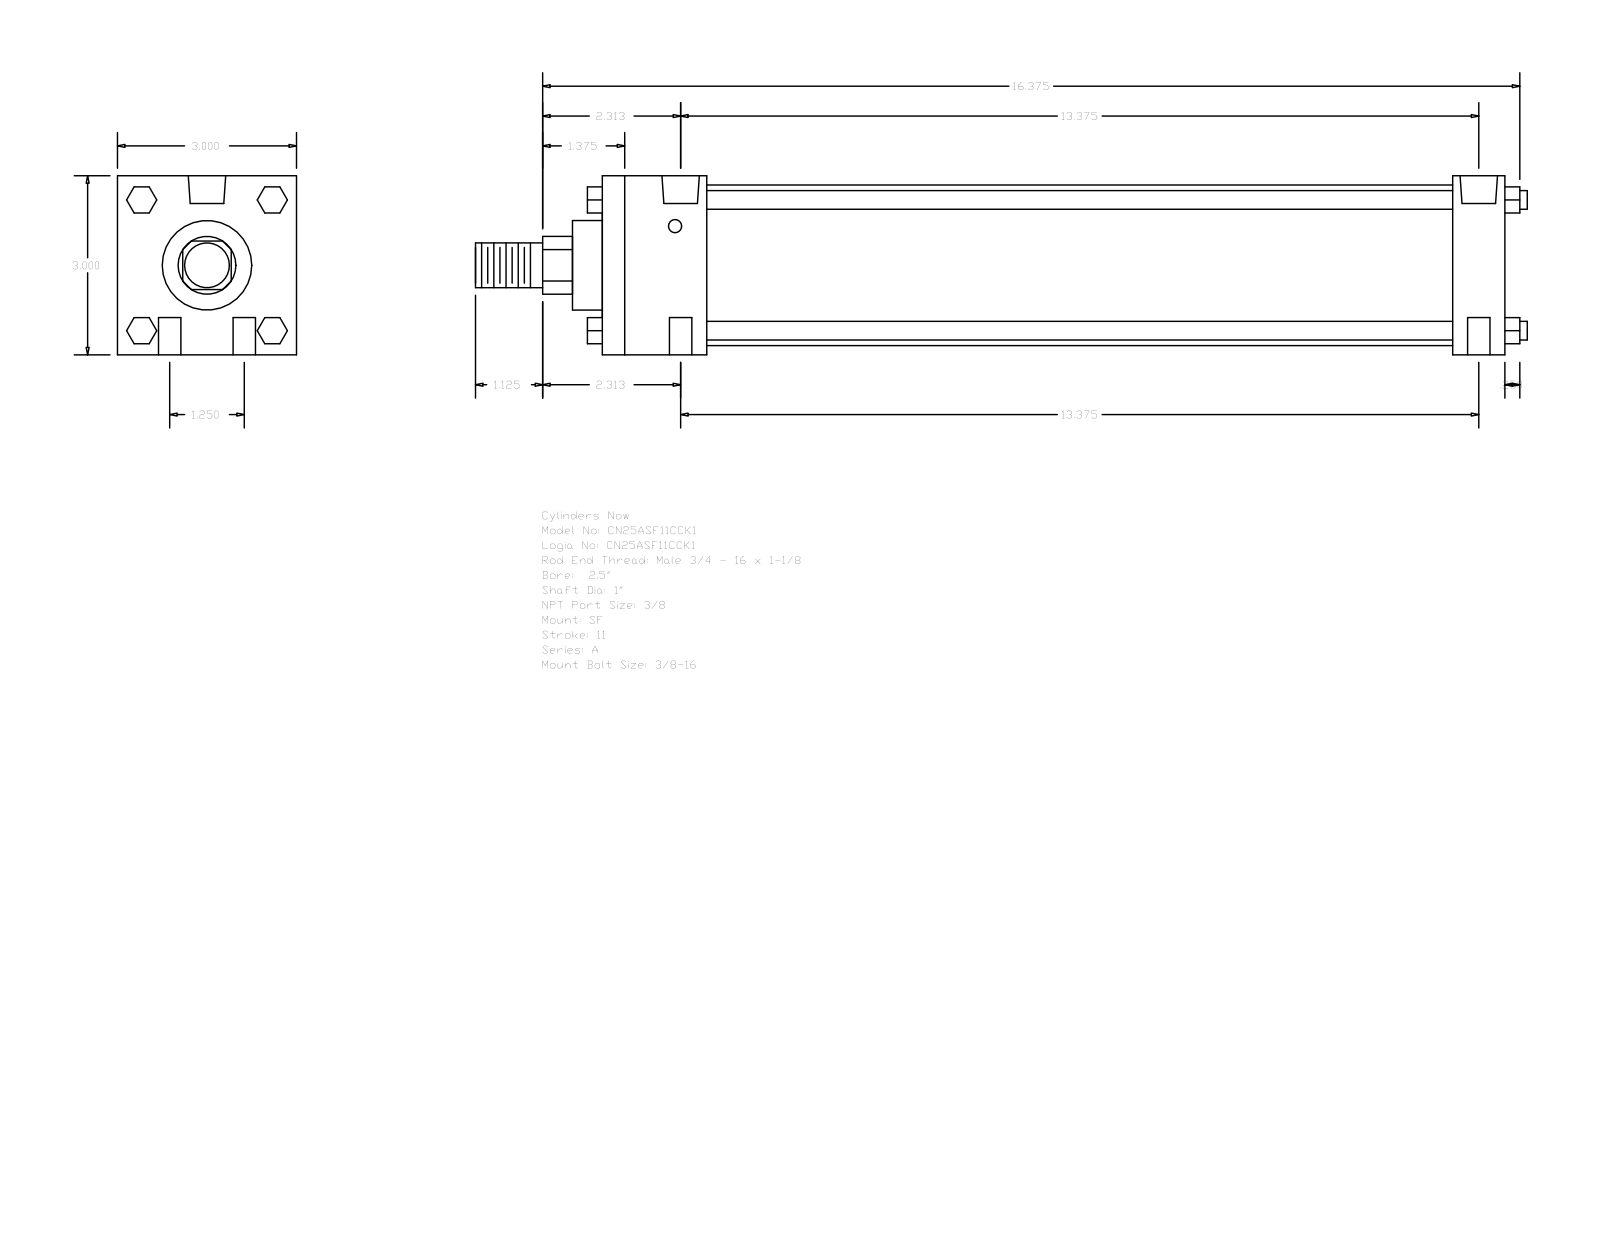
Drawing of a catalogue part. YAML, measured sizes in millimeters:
part_name: "A_SF__0250_1"
step_written_by: "GSSL Pune (CONFIG_CONTROL_DESIGN)"
units: millimeters
bodies: {solids: 0, faces: 124, planar: 94, cylindrical: 30, other: 0}
overall_size: [447.68, 76.2, 76.2]
round_holes:
  - {diameter: 9.53, count: 4}
  - {diameter: 5.56, count: 2}
  - {diameter: 15.93, count: 2}
round_bosses_or_shafts:
  - {diameter: 7.94, count: 4}
  - {diameter: 68.33, count: 1}
  - {diameter: 38.1, count: 1}
  - {diameter: 25.4, count: 1}
  - {diameter: 19.05, count: 1}
partial_cylinders:
  - {radius: 12.29, count: 1}
face_to_face_distances: [76.2, 384.17, 361.95, 22.22, 44.45, 317.5, 339.72, 12.7, 11.11, 57.15]
hole_center_spacings: [15.88, 340.09, 339.72, 31.76, 341.2, 344.48]
